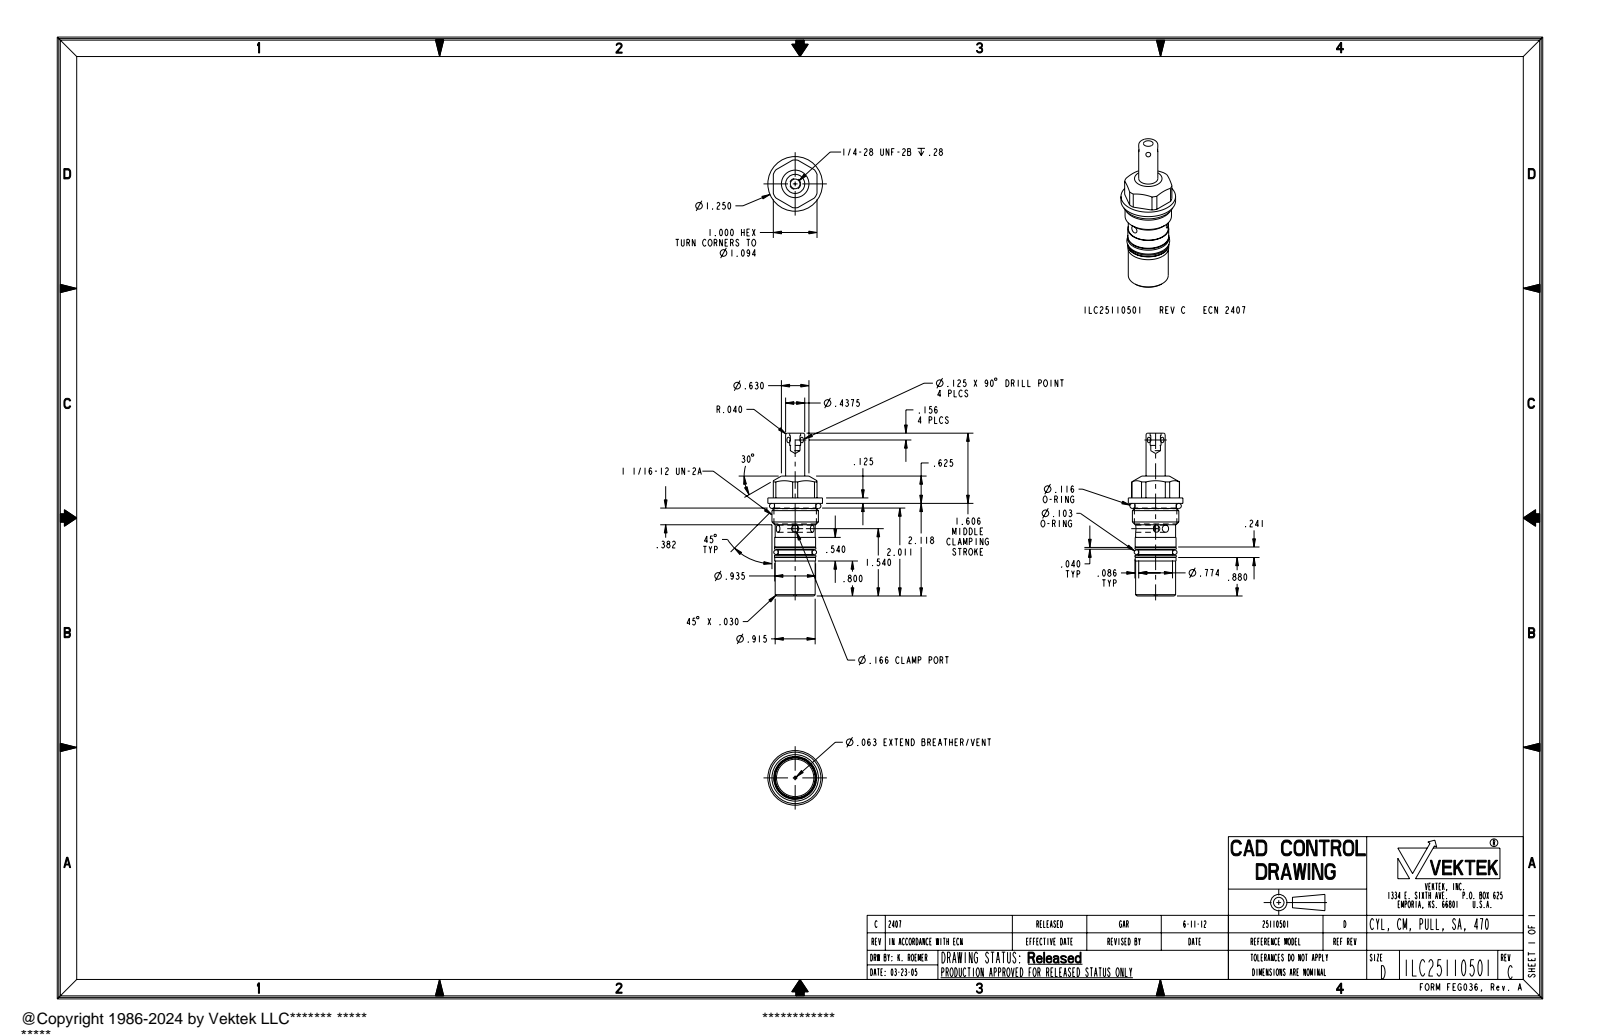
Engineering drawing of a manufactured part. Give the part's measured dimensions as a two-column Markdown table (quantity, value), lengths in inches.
| quantity | value |
| --- | --- |
| part name | ILC25110501 |
| STEP written by | PRO/ENGINEER BY PARAMETRIC TECHNOLOGY CORPORATION, 2007460 (AUTOMOTIVE_DESIGN_CC2) |
| units | inches |
| bodies | 3 solids, 99 faces (25 planar, 46 cylindrical, 28 other) |
| overall size | 3.724 × 1.25 × 1.25 |
| volume | 2.16 in³ |
| surface area | 17.7 in² |
| round holes (diameter × count) | 0.166 × 3, 0.063 × 1, 0.221 × 1 |
| round bosses / shafts (diameter × count) | 1.25 × 1, 1.063 × 1, 0.972 × 1, 0.946 × 1, 0.945 × 1, 0.935 × 1, 0.915 × 1, 0.774 × 1 |
| partial cylindrical surfaces (radius × count) | 0.547 × 1 |
| main face-to-face distances | 2.118, 1, 0.05, 0.191, 2.243, 0.125, 0.89, 0.93, 1.07, 1.111 |
